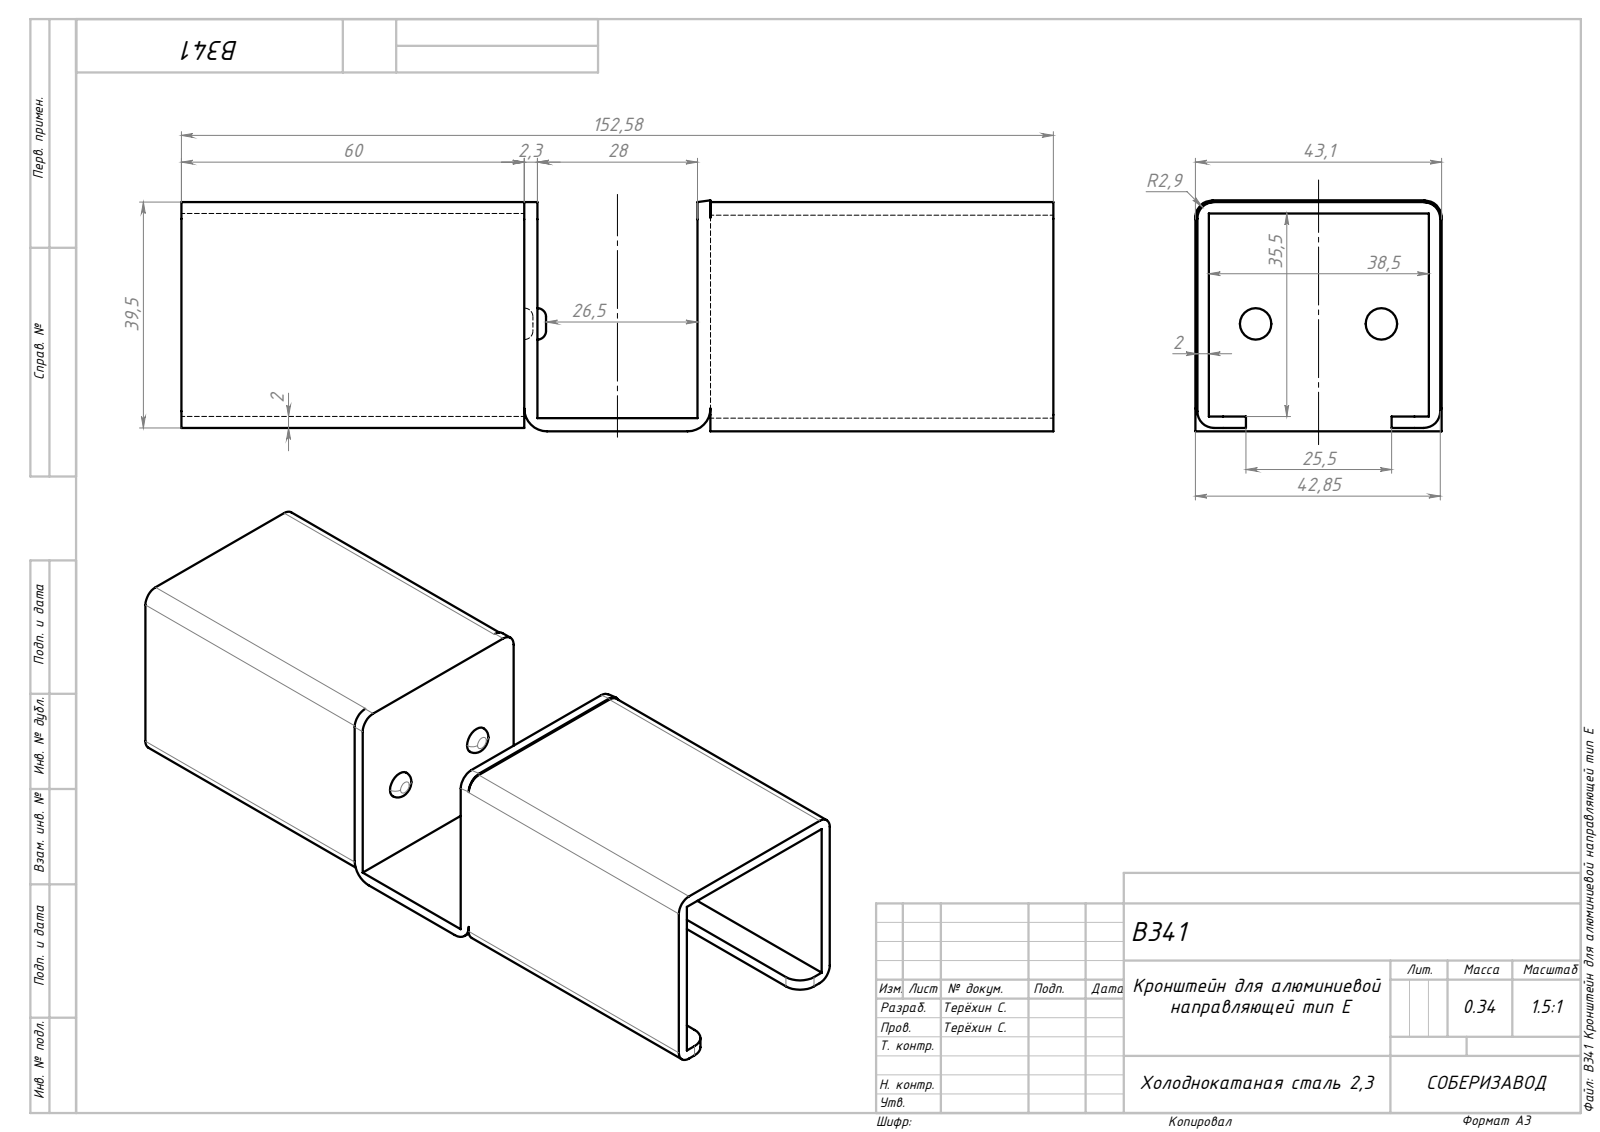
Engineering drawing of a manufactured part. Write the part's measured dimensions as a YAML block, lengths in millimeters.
part_name: "B341 Кронштейн для алюминиевой направляющей тип E_00; B341 Кронштейн для алюминиевой направляющей тип E"
step_written_by: "SolidWorks 2022 (AUTOMOTIVE_DESIGN)"
units: millimeters
bodies: {solids: 1, faces: 74, planar: 44, cylindrical: 22, other: 8}
overall_size: [152.58, 43.1, 40.4]
volume: 43218
surface_area: 41284
partial_cylinders:
  - {radius: 4, count: 10}
  - {radius: 2.9, count: 8}
  - {radius: 3, count: 4}
face_to_face_distances: [2.3, 2, 40.8, 38.5, 40.5, 37.8, 35.5, 43.1, 40.75, 38.45]
